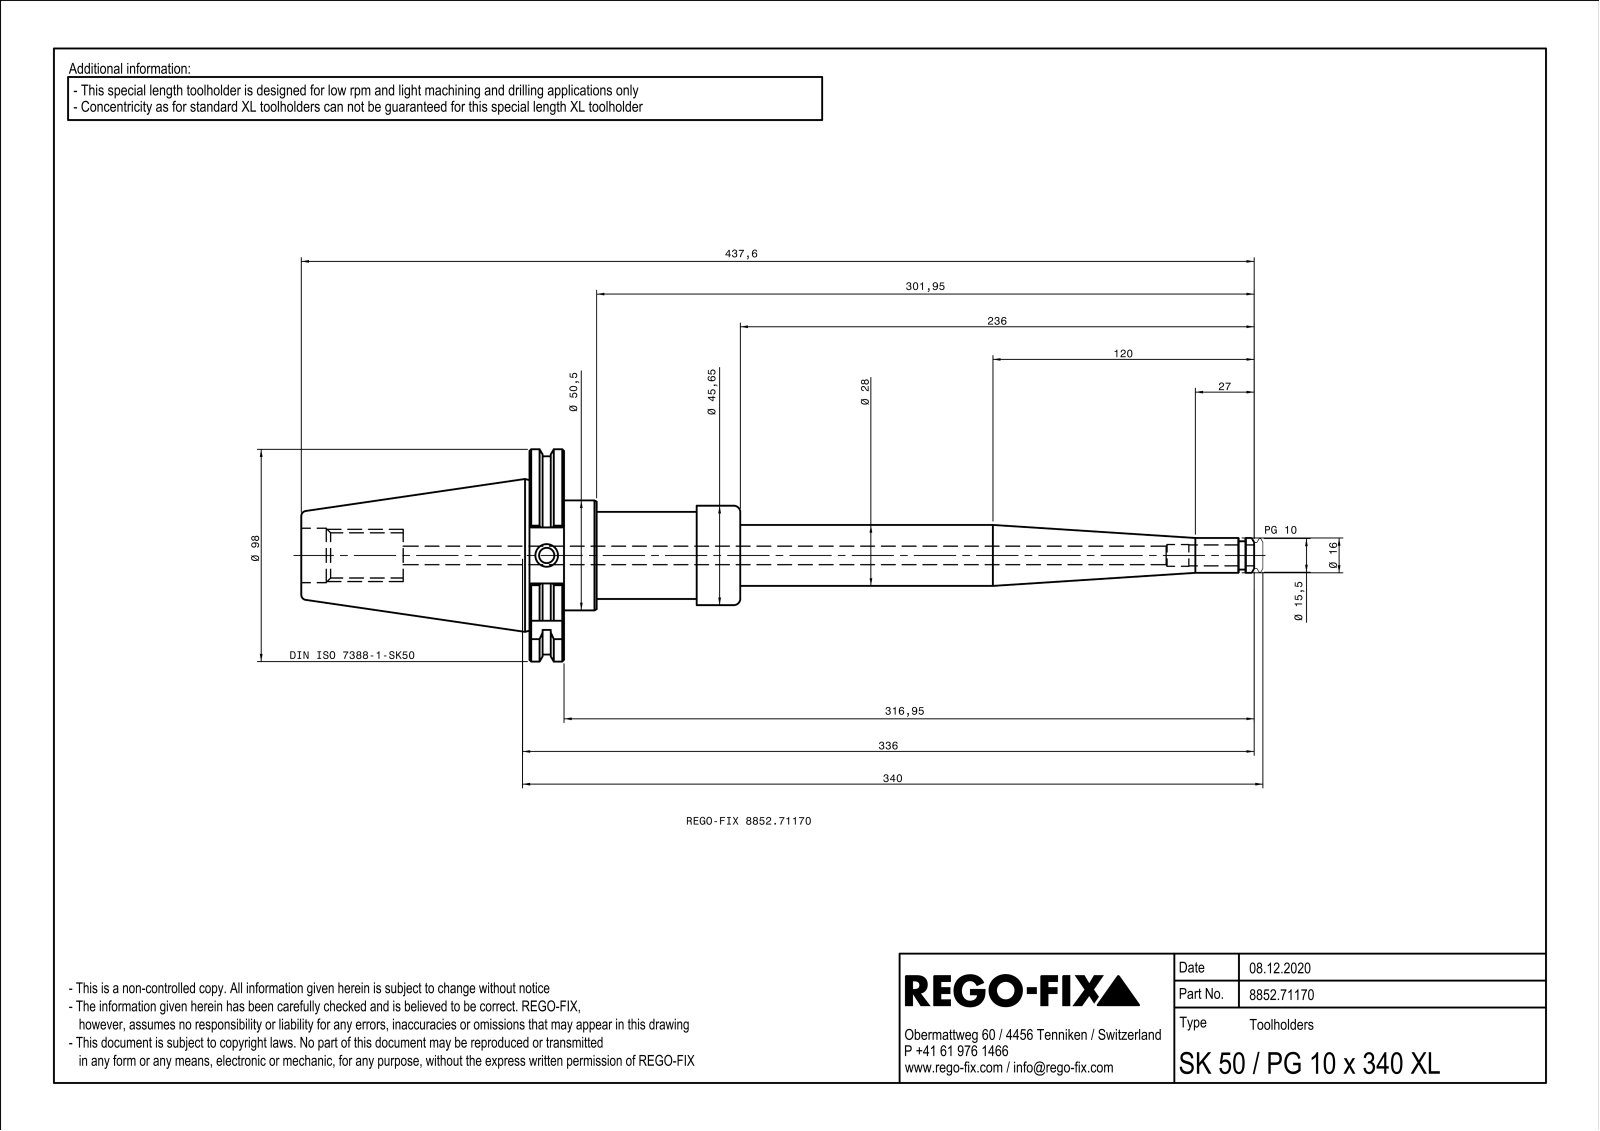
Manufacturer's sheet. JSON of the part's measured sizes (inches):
{"part_name": "NOCUT", "step_written_by": "SIEMENS PLM Software Solid Edge ST10 (AUTOMOTIVE_DESIGN)", "units": "inches", "bodies": {"solids": 1, "faces": 168, "planar": 58, "cylindrical": 39, "other": 71}, "overall_size": [17.228, 3.839, 3.684], "volume_in3": 31.71, "surface_area_in2": 138.7, "round_holes": [[0.394, 2], [0.276, 1], [0.354, 1], [0.817, 1], [0.984, 1], [1.142, 1], [1.511, 1], [1.577, 1], [1.705, 1]], "round_bosses_or_shafts": [[3.583, 1], [1.988, 1], [1.797, 1], [1.575, 1], [1.339, 1], [1.299, 1], [1.102, 1], [0.972, 1]], "partial_cylinders_radius": [[0.02, 5], [0.896, 1], [1.919, 1]], "face_to_face_distances": [0.624, 3.187, 3.811, 7.937, 4.75, 4.126, 0.236, 0.551, 2.596, 0.591]}
